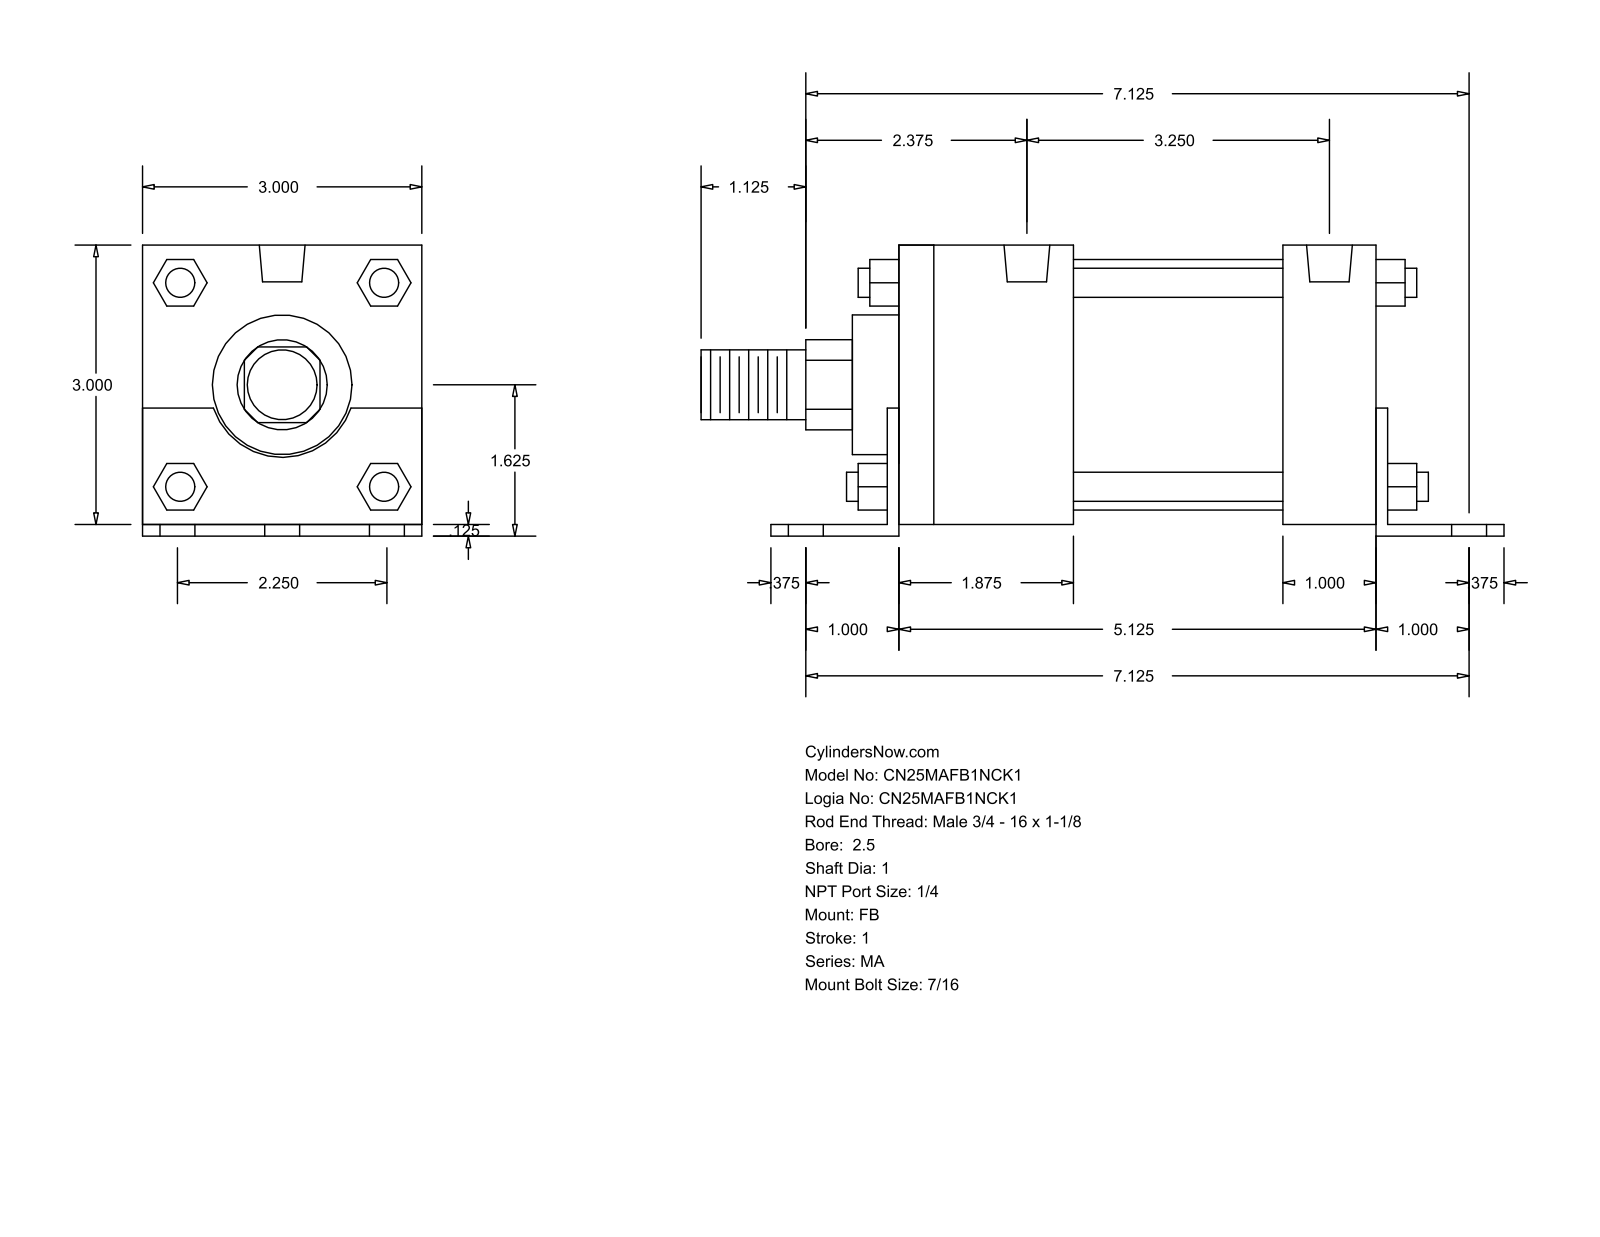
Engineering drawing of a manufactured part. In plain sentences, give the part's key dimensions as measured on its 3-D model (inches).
The part is named "MA_FB__0250_1". Its 3-D file was written by "GSSL Pune (CONFIG_CONTROL_DESIGN)". It is 0 solids with 140 faces: 105 planar, 35 cylindrical and 0 other. Overall it measures 8.625 by 3.125 by 3 inches. Round holes: 6 of diameter 0.437, 4 of diameter 0.313, 2 of diameter 0.492. Round bosses or shafts: 4 of diameter 0.313, 1 of diameter 2.69, 1 of diameter 1.5, 1 of diameter 1, 1 of diameter 0.75. Partial cylindrical surfaces (rounded edges, fillets, slot ends): 1 of radius 0.484, 1 of radius 0.78. The main face-to-face distances are 3, 0.125, 3.125, 5.125, 0.125, 0.5, 5.25, 1.125, 2, 1.875. The hole center spacings are 1.125, 7.213, 7.125, 1.874, 2.25, 2.628, 3.25, 4.881.
